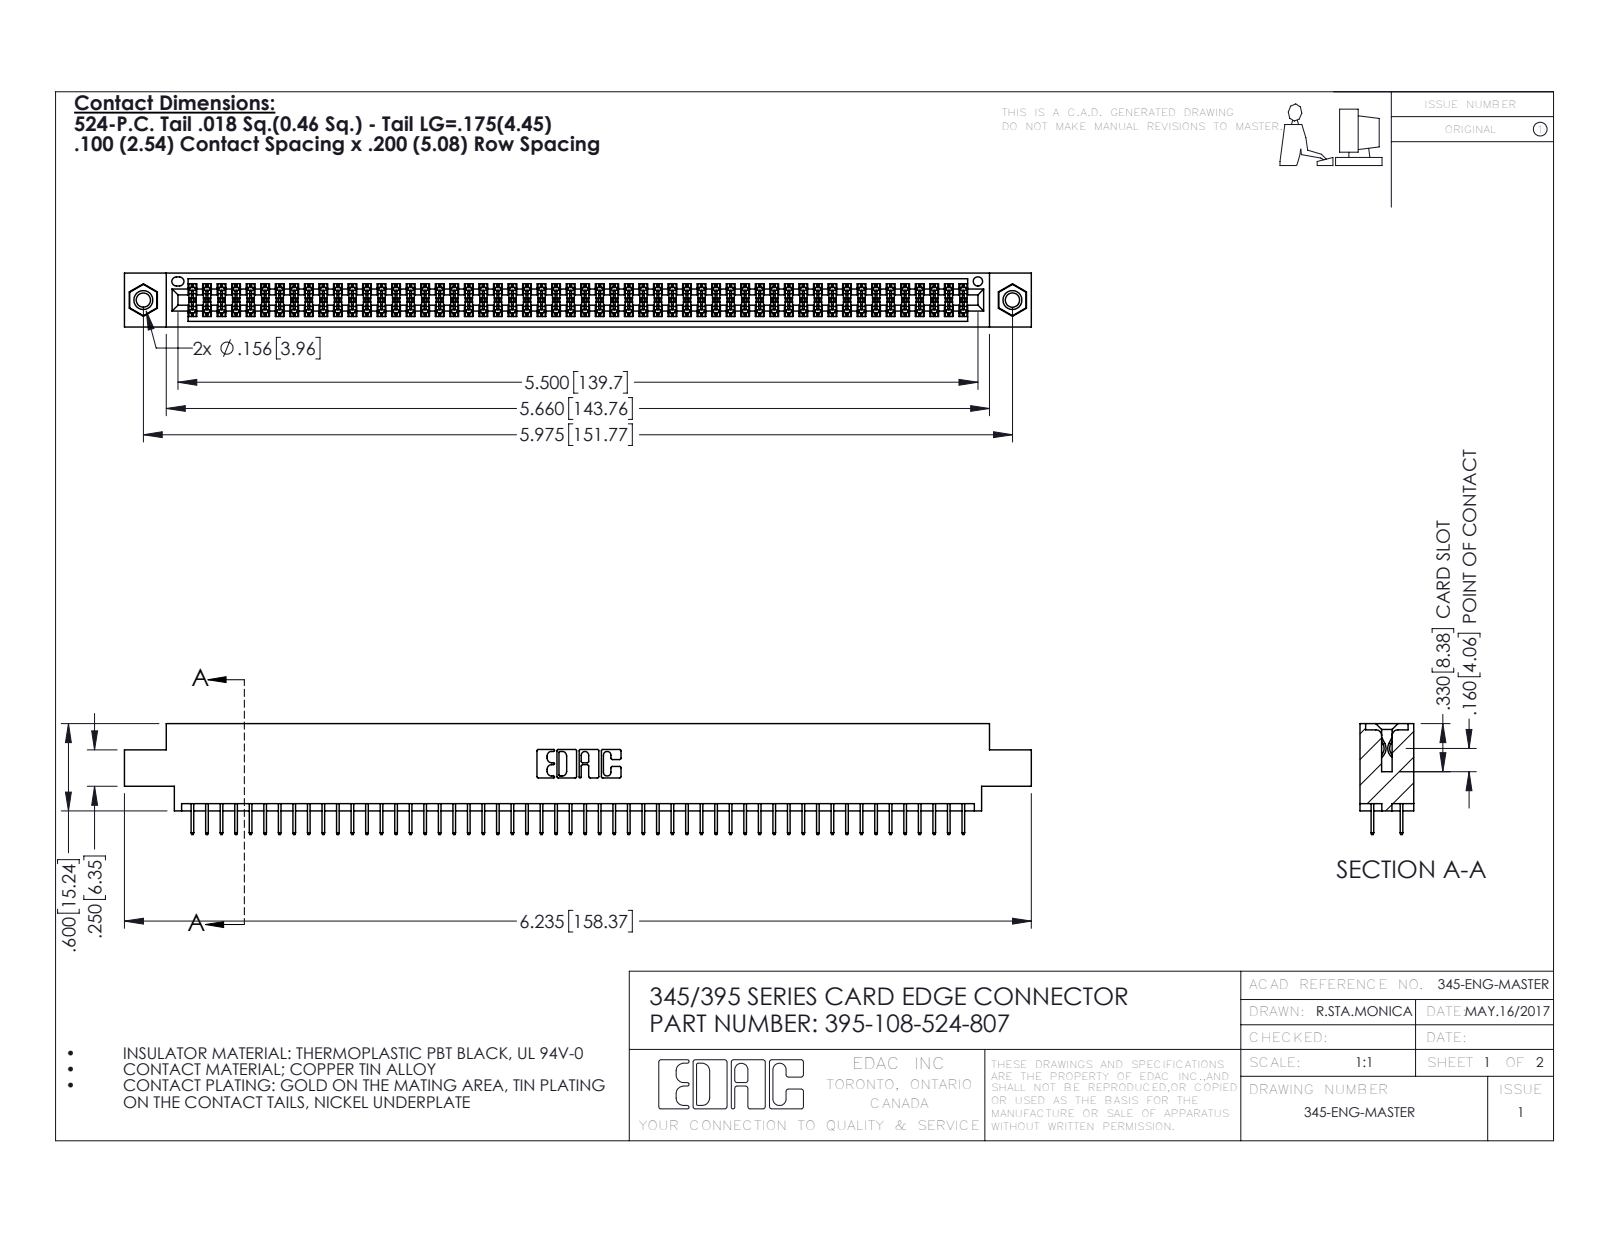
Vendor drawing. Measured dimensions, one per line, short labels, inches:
name: 345-250-001_345-250-005-103; 345-292-001_345-293-124; 345 Part_0.170 Offset - 0.156 Dia-TI; 395-108-524-807
written by: SolidWorks 2016 (CONFIG_CONTROL_DESIGN)
unit: in
bodies: 111 solids, 6022 faces (4328 planar, 1678 cylindrical, 16 other)
size: 6.235 × 0.762 × 0.37
volume: 0.928 in³; area: 34.79 in²
holes: 2× ⌀0.098, 2× ⌀0.125, 2× ⌀0.156, 1× ⌀0.064
bosses: 2× ⌀0.155
rounds: 162× R0.006, 22× R0.01, 6× R0.007, 6× R0.031, 3× R0.026, 2× R0.014, 2× R0.019, 2× R0.022
face distances: 0.072, 0.298, 0.37, 0.2, 0.098, 0.272, 0.025, 0.225, 0.072, 0.175
hole spacings: 0.27, 5.739, 5.975
